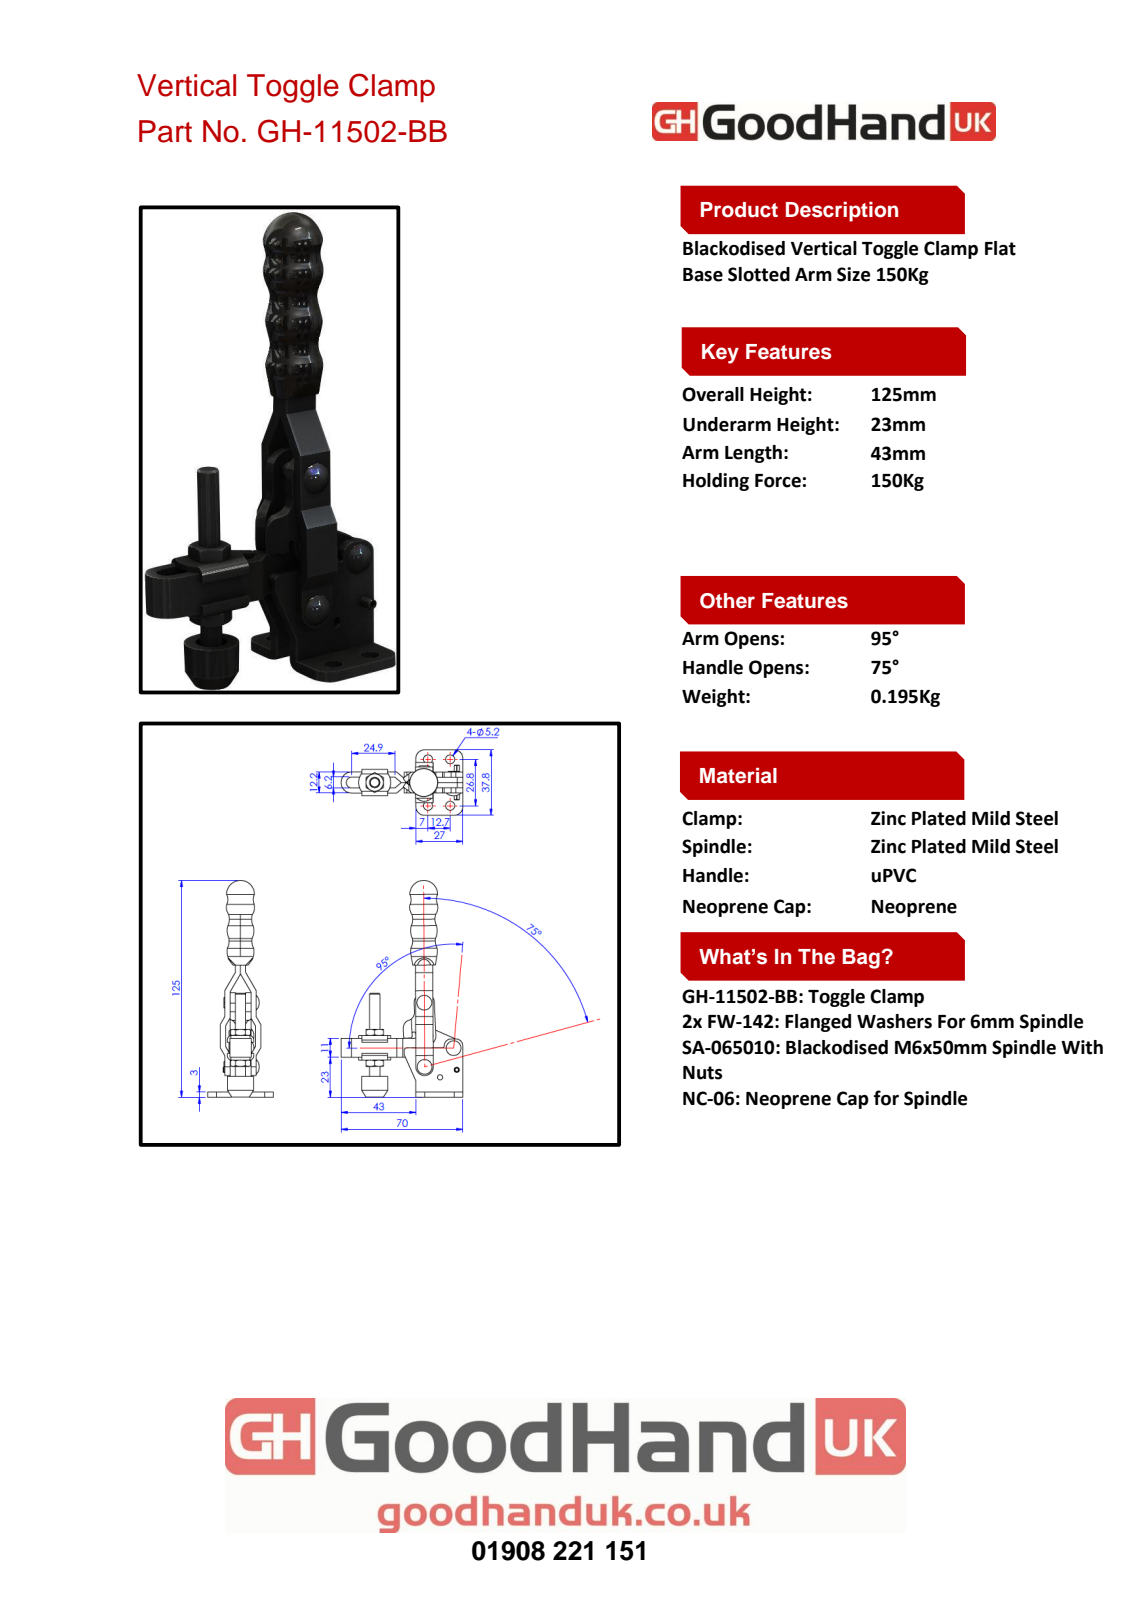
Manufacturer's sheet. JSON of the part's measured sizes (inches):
{"part_name": "111502B13; GH-SA-065010; GH-11502-BB; GH-NC-06 (+8 more)", "step_written_by": "SolidWorks 2016 (AUTOMOTIVE_DESIGN)", "units": "inches", "bodies": {"solids": 18, "faces": 419, "planar": 163, "cylindrical": 153, "other": 103}, "overall_size": [4.922, 2.756, 1.488], "volume_in3": 1.603, "surface_area_in2": 44.08, "round_holes": [[0.157, 4], [0.205, 4], [0.19, 3], [0.118, 2], [0.079, 1], [0.191, 1], [0.197, 1], [0.236, 1], [0.248, 1], [0.335, 1], [0.453, 1]], "round_bosses_or_shafts": [[0.189, 4], [0.591, 1], [0.295, 1], [0.236, 1], [0.191, 1]], "partial_cylinders_radius": [[0.039, 9], [0.197, 7], [0.102, 4], [0.059, 2], [0.079, 2], [0.118, 2], [0.157, 2], [0.209, 2]], "face_to_face_distances": [0.118, 0.236, 0.354, 0.472, 0.122, 0.24, 0.358, 0.476, 0.114, 0.394], "hole_center_spacings": [0.5, 1.055, 1.168, 1.317, 1.786, 0.414, 0.422, 0.497]}
